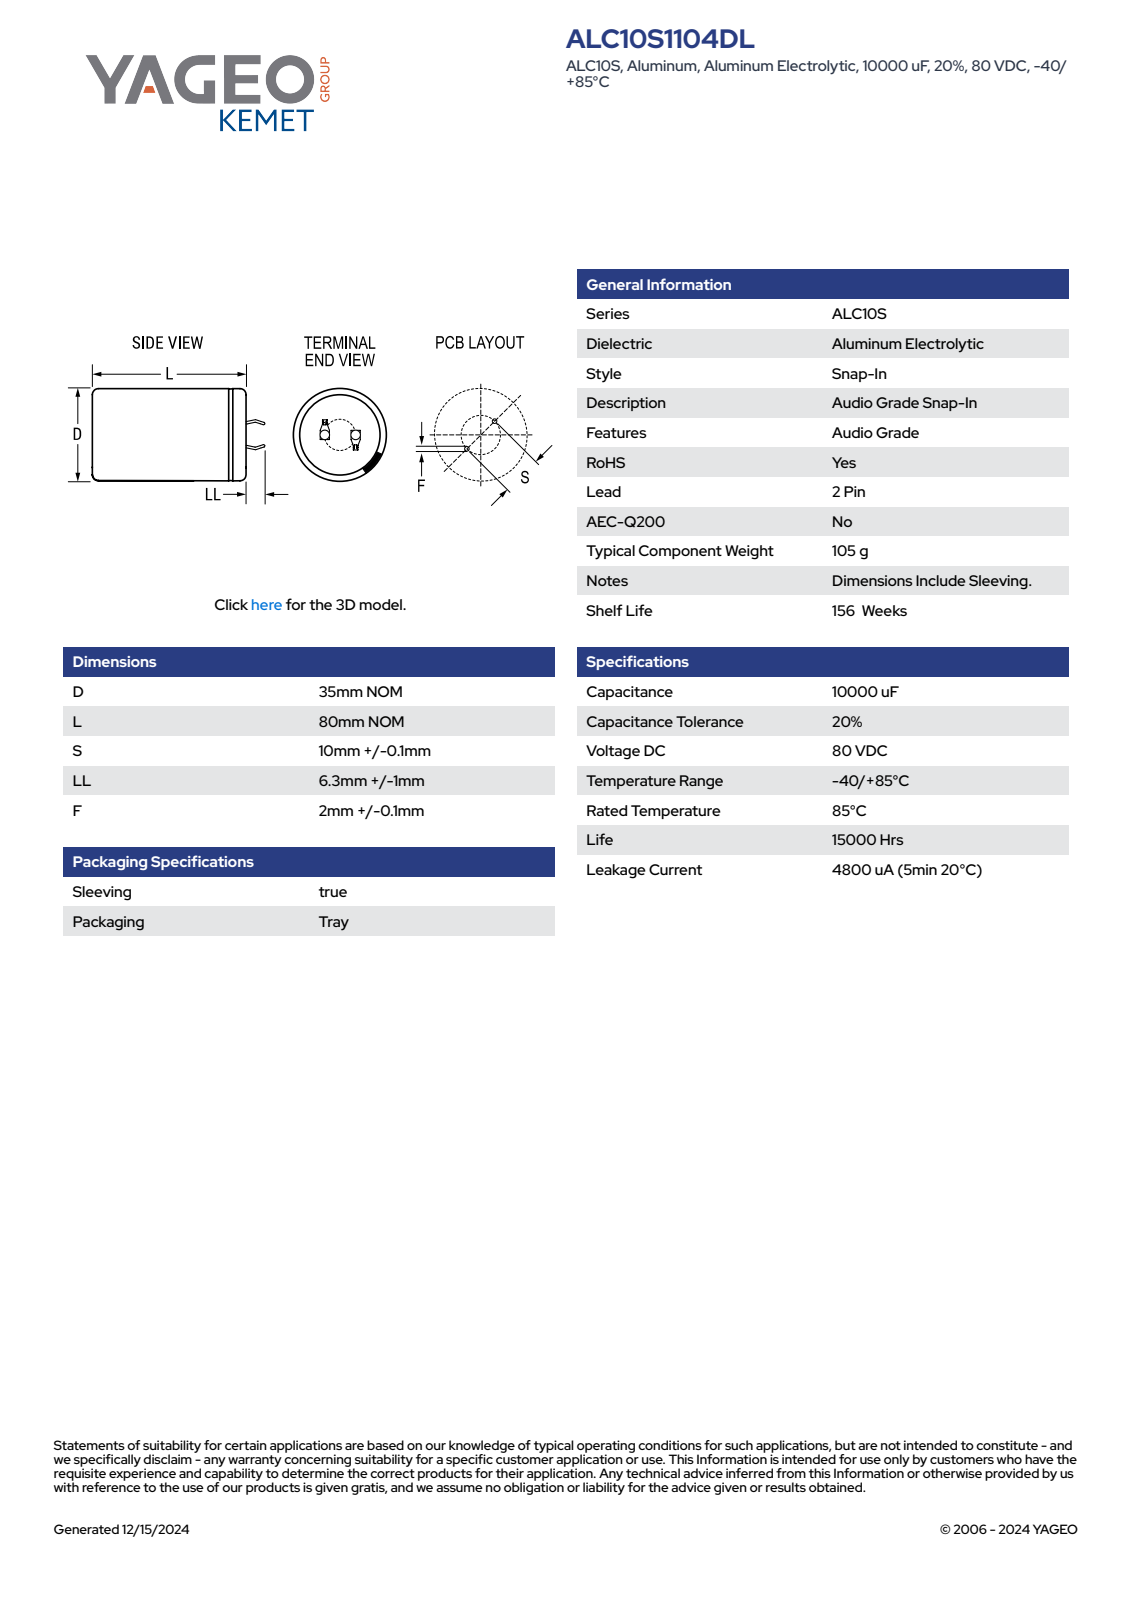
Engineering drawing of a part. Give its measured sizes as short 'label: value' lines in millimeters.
name: CARS_K2P_35X80_D35L80S10LL7.3F2.1
written by: SolidWorks 2014 (AUTOMOTIVE_DESIGN)
unit: mm
bodies: 1 solid, 100 faces (52 planar, 9 cylindrical, 39 other)
size: 87.29 × 35 × 35
volume: 76 485 mm³; area: 10 721 mm²
holes: 1× ⌀30.97
bosses: 1× ⌀35
rounds: 1× R17.49
face distances: 79.99, 0.6, 80.49, 0.5, 7.08, 7.64, 0.75, 1.35, 7.68, 6.48
